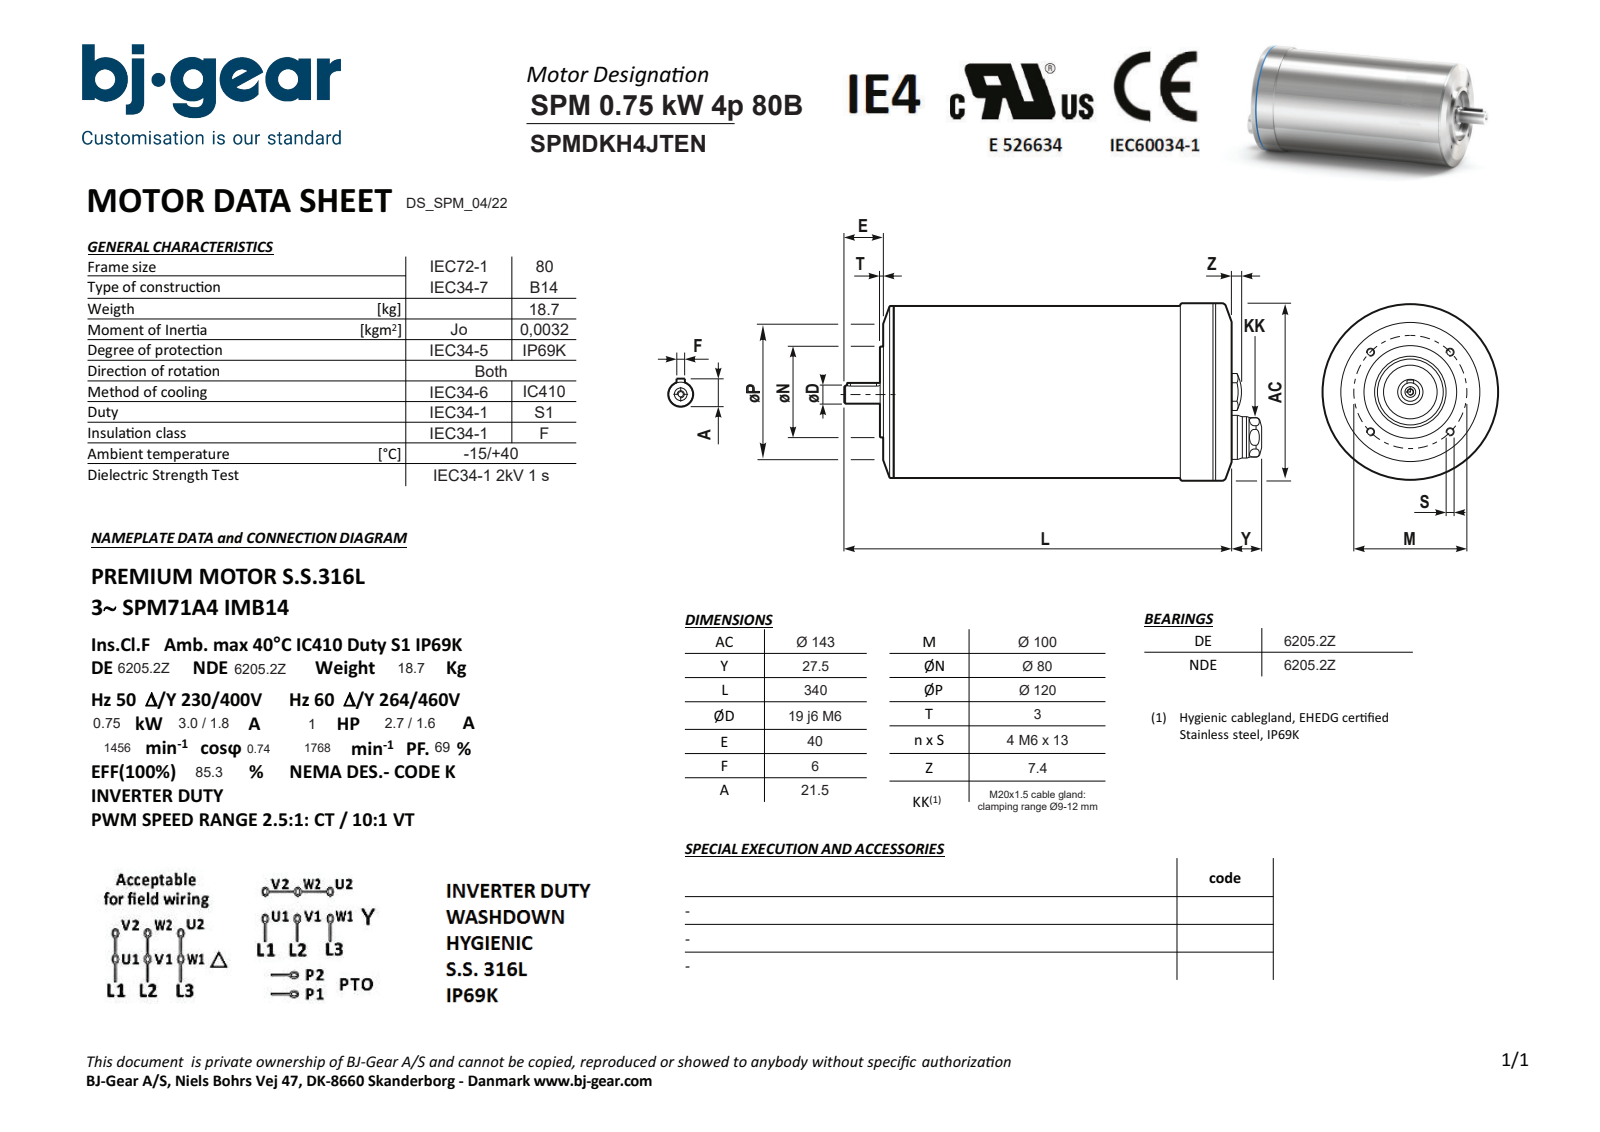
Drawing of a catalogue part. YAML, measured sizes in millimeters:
part_name: "SPMDKH4JTENN4KSA1-N---NNN"
step_written_by: "Solid Edge (AUTOMOTIVE_DESIGN)"
units: millimeters
bodies: {solids: 1, faces: 87, planar: 30, cylindrical: 32, other: 25}
overall_size: [367.5, 143, 143]
volume: 4570000
surface_area: 168444
round_holes:
  - {diameter: 4.92, count: 5}
  - {diameter: 6.4, count: 1}
  - {diameter: 7, count: 1}
  - {diameter: 13.4, count: 1}
  - {diameter: 68, count: 1}
round_bosses_or_shafts:
  - {diameter: 143, count: 1}
  - {diameter: 142.98, count: 1}
  - {diameter: 139, count: 1}
  - {diameter: 138.98, count: 1}
  - {diameter: 80, count: 1}
  - {diameter: 25, count: 1}
  - {diameter: 20, count: 1}
  - {diameter: 19, count: 1}
partial_cylinders:
  - {radius: 3, count: 2}
  - {radius: 12.8, count: 1}
face_to_face_distances: [300, 6, 294, 9, 303, 3, 24, 340, 46, 40]
hole_center_spacings: [50.01, 70.72, 35.46, 81.44, 100.01, 38]
